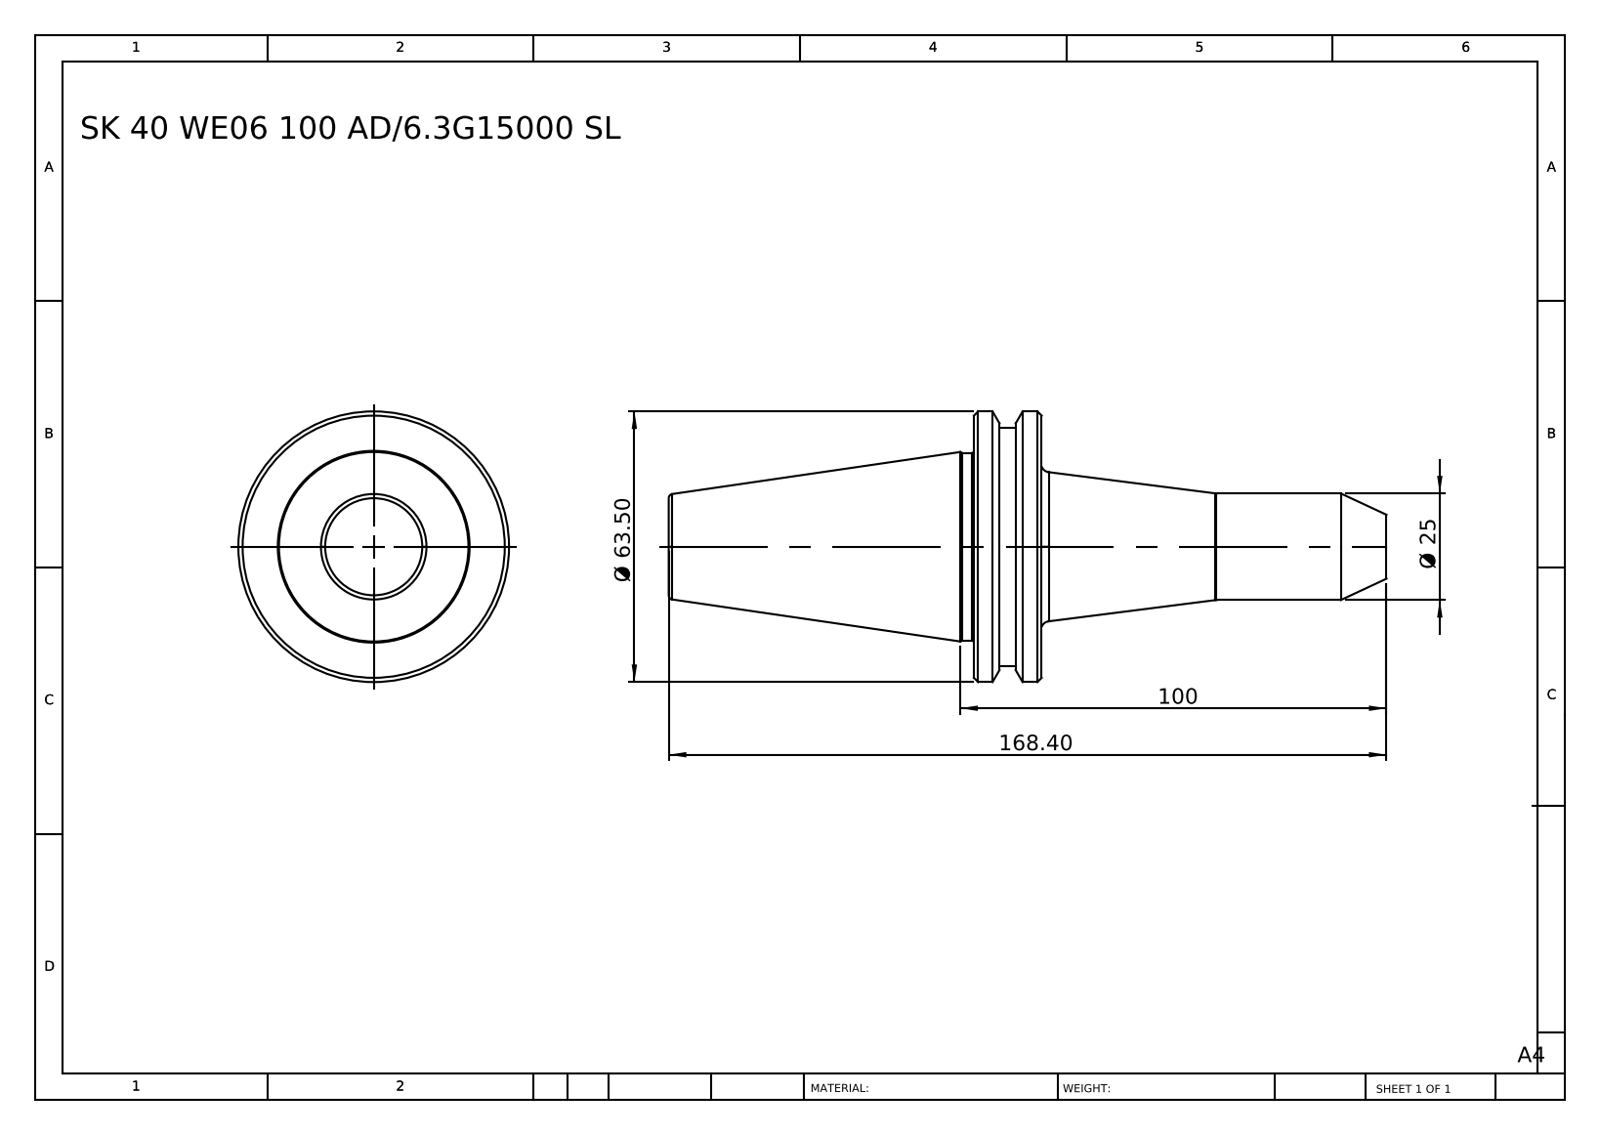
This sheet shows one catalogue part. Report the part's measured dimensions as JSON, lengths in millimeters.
{"part_name": "SK40 WE06 100 AD-6.3G15000 SL", "step_written_by": "SolidWorks 2014 (CONFIG_CONTROL_DESIGN)", "units": "millimeters", "bodies": {"solids": 1, "faces": 40, "planar": 6, "cylindrical": 10, "other": 24}, "overall_size": [168.4, 63.5, 63.5], "volume_mm3": 164566, "surface_area_mm2": 23027, "round_bosses_or_shafts": [[63.5, 1], [56, 1], [44, 1], [25, 1]], "face_to_face_distances": [15.9, 87.5, 71.6, 80.9, 96.8, 168.4, 90.8, 9.9, 6, 77.6]}
